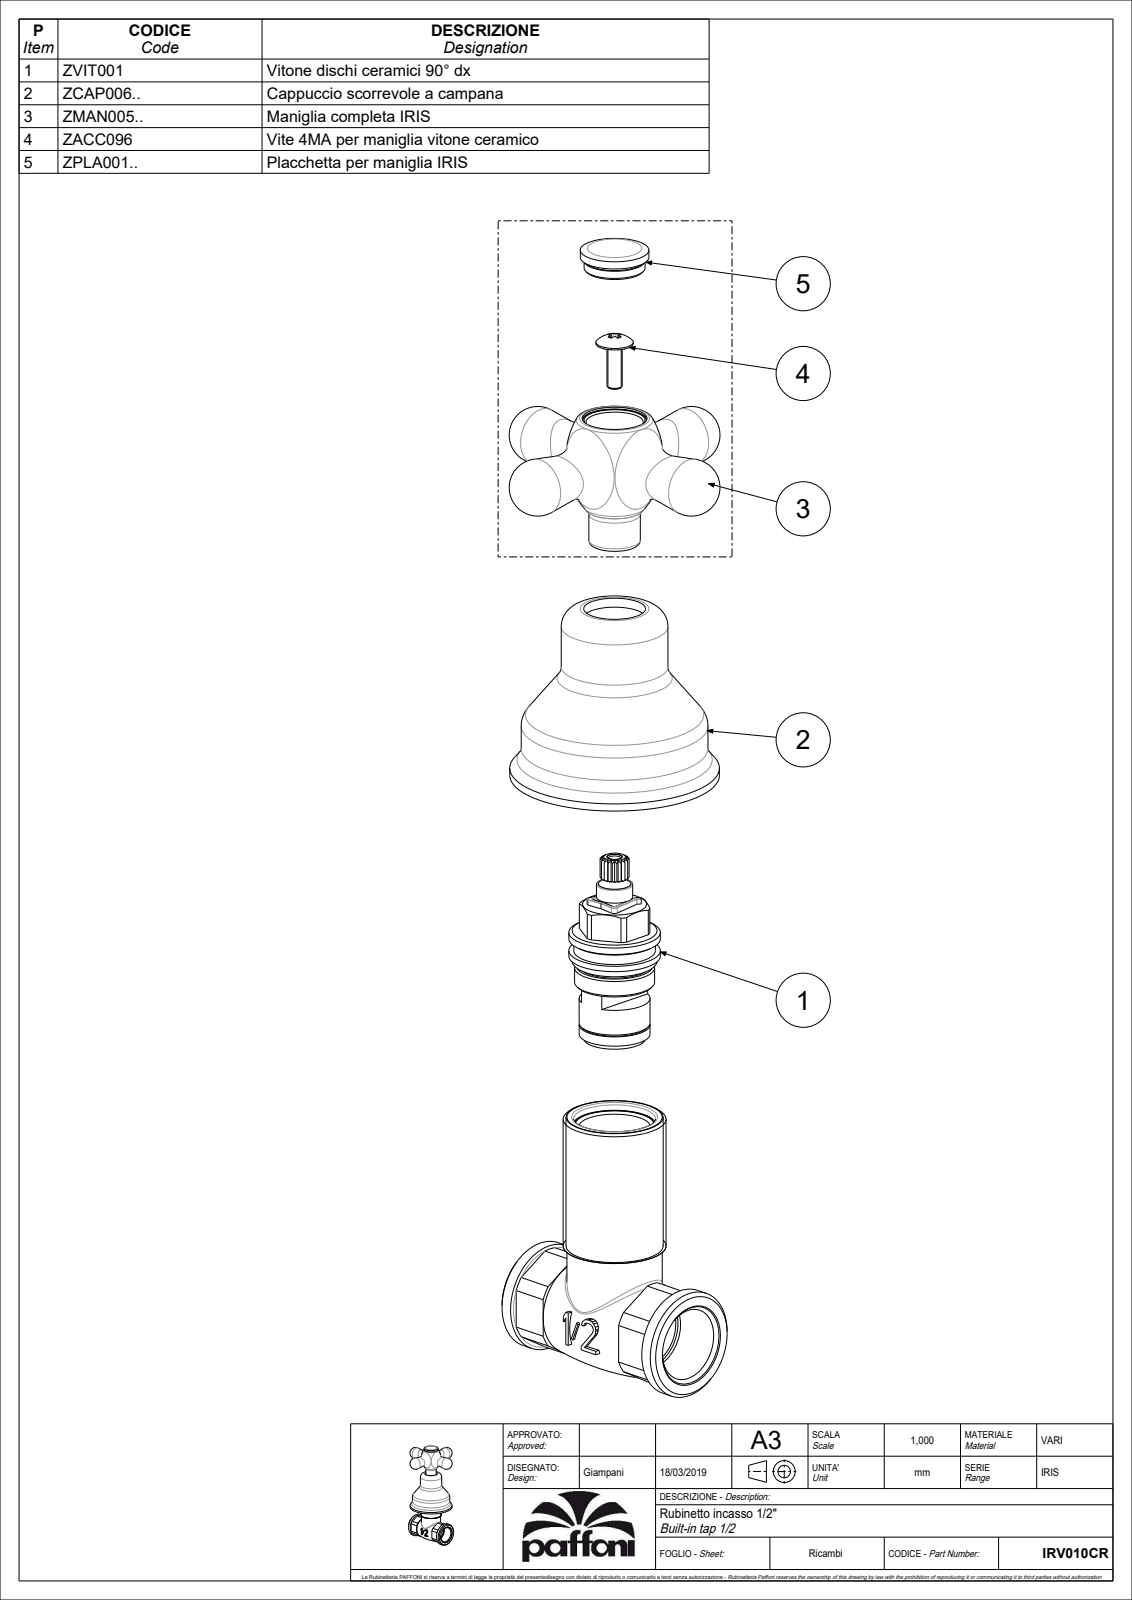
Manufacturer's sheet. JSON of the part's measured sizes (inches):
{"part_name": "IRV010CR", "step_written_by": "CREO PARAMETRIC BY PTC INC, 2020044 (CONFIG_CONTROL_DESIGN)", "units": "inches", "bodies": {"solids": 1, "faces": 67, "planar": 3, "cylindrical": 10, "other": 54}, "overall_size": [3.276, 2.835, 2.835], "volume_in3": 5.055, "surface_area_in2": 23.53, "round_bosses_or_shafts": [[2.165, 1], [1.929, 1], [1.102, 1], [0.709, 1], [0.531, 1]], "face_to_face_distances": [1.831, 3.138, 1.307]}
